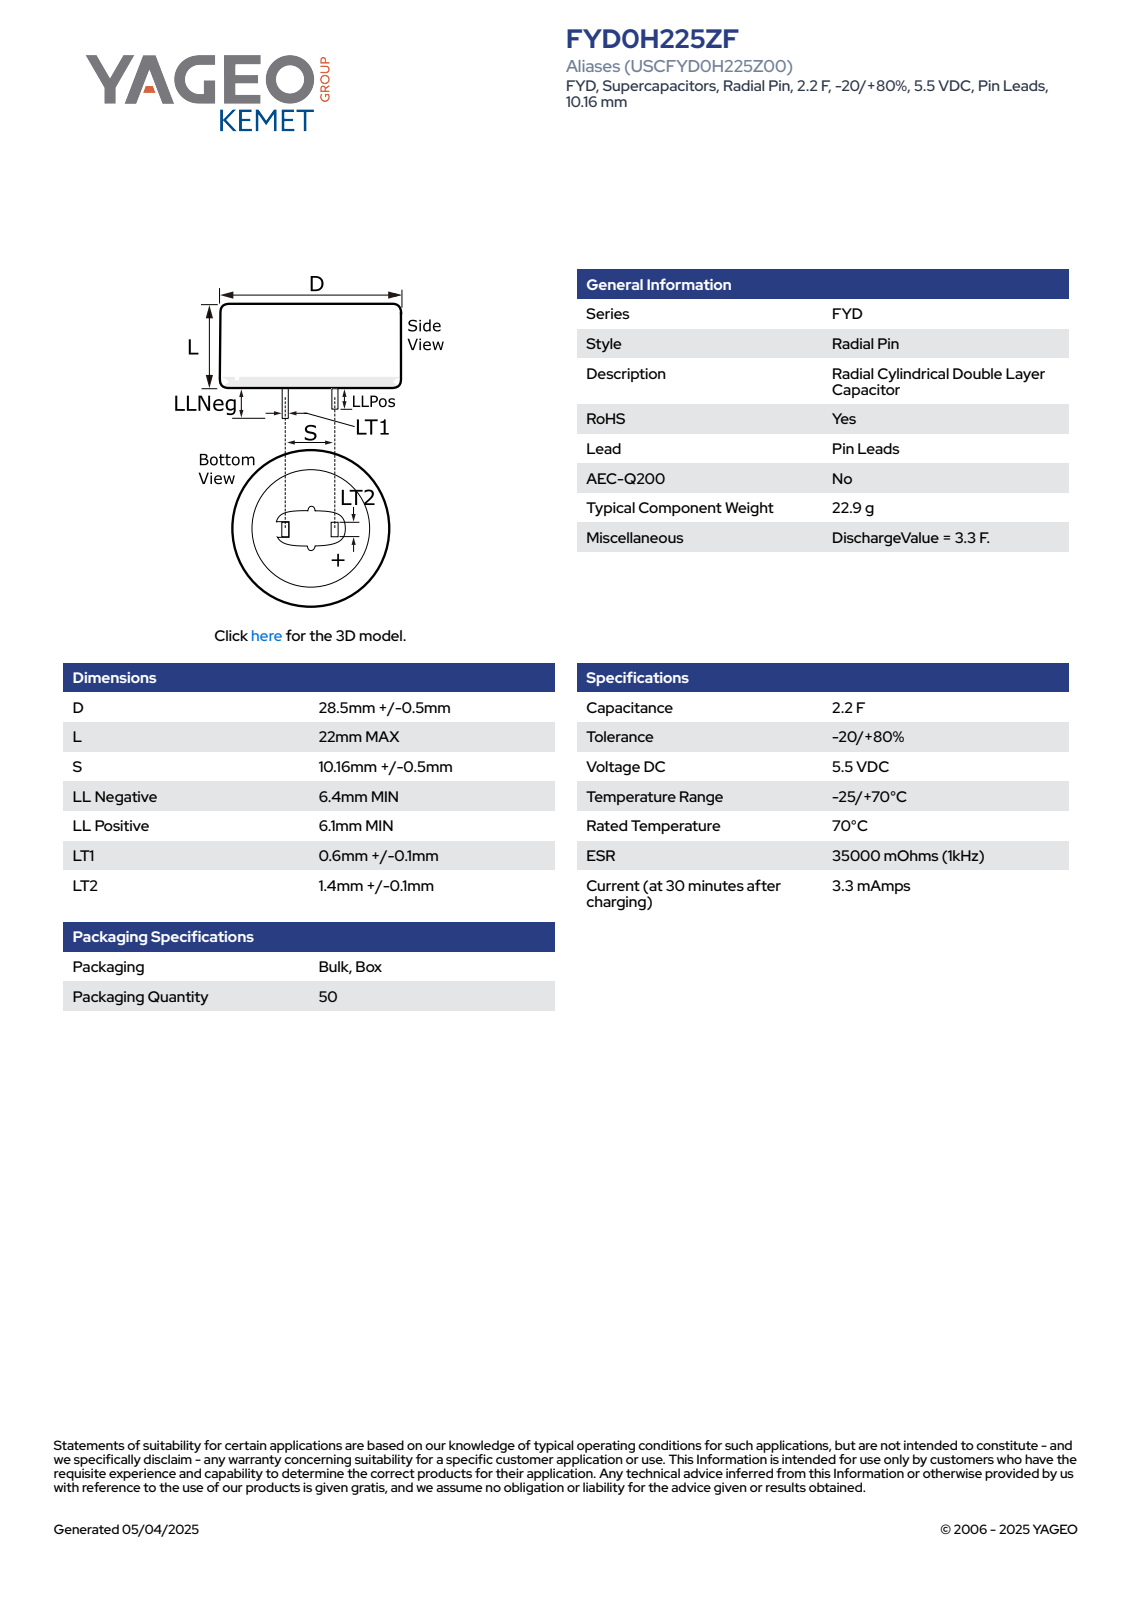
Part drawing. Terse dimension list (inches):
name: CDR_LPLLN_D29L22S10.16LLNEG6.4LLPOS6.1LT10.7LT21.5
written by: SolidWorks 2014 (AUTOMOTIVE_DESIGN)
unit: in
bodies: 1 solid, 78 faces (70 planar, 4 cylindrical, 4 other)
size: 1.142 × 1.142 × 1.118
volume: 0.883 in³; area: 5.065 in²
bosses: 1× ⌀1.142
rounds: 1× R0.571
face distances: 0.866, 0.028, 0.4, 0.866, 0.428, 0.372, 0.059, 0.252, 1.118, 1.118
